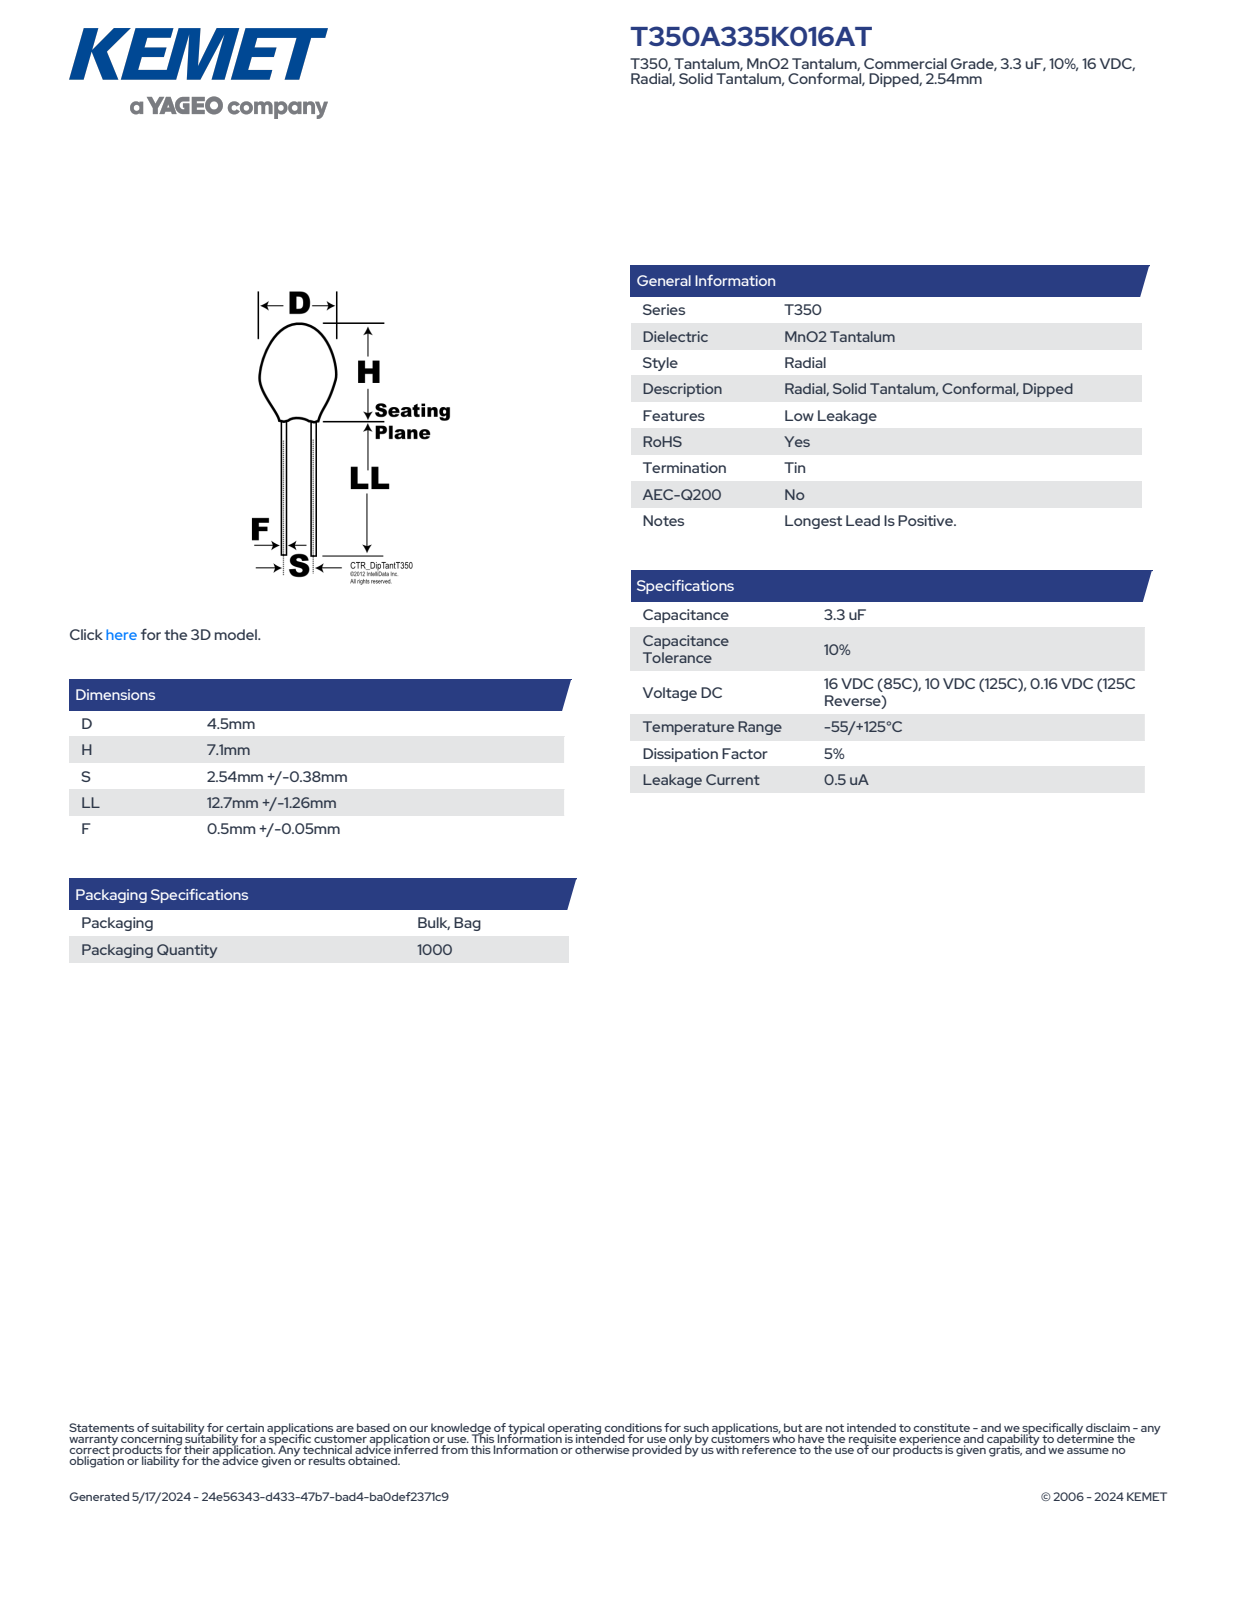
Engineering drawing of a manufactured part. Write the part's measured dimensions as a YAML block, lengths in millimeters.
part_name: "CTR_T350_D4.5H7.1S2.54LL13.96F0.55"
step_written_by: "SolidWorks 2014 (AUTOMOTIVE_DESIGN)"
units: millimeters
bodies: {solids: 1, faces: 73, planar: 26, cylindrical: 10, other: 37}
overall_size: [21.06, 4.5, 4.5]
volume: 104
surface_area: 159
round_bosses_or_shafts:
  - {diameter: 0.55, count: 2}
  - {diameter: 4.5, count: 1}
partial_cylinders:
  - {radius: 2.24, count: 1}
face_to_face_distances: [7.1, 13.96, 21.06, 17.84, 3.88, 3.22, 17.23, 3.27, 0.61, 3.83]
